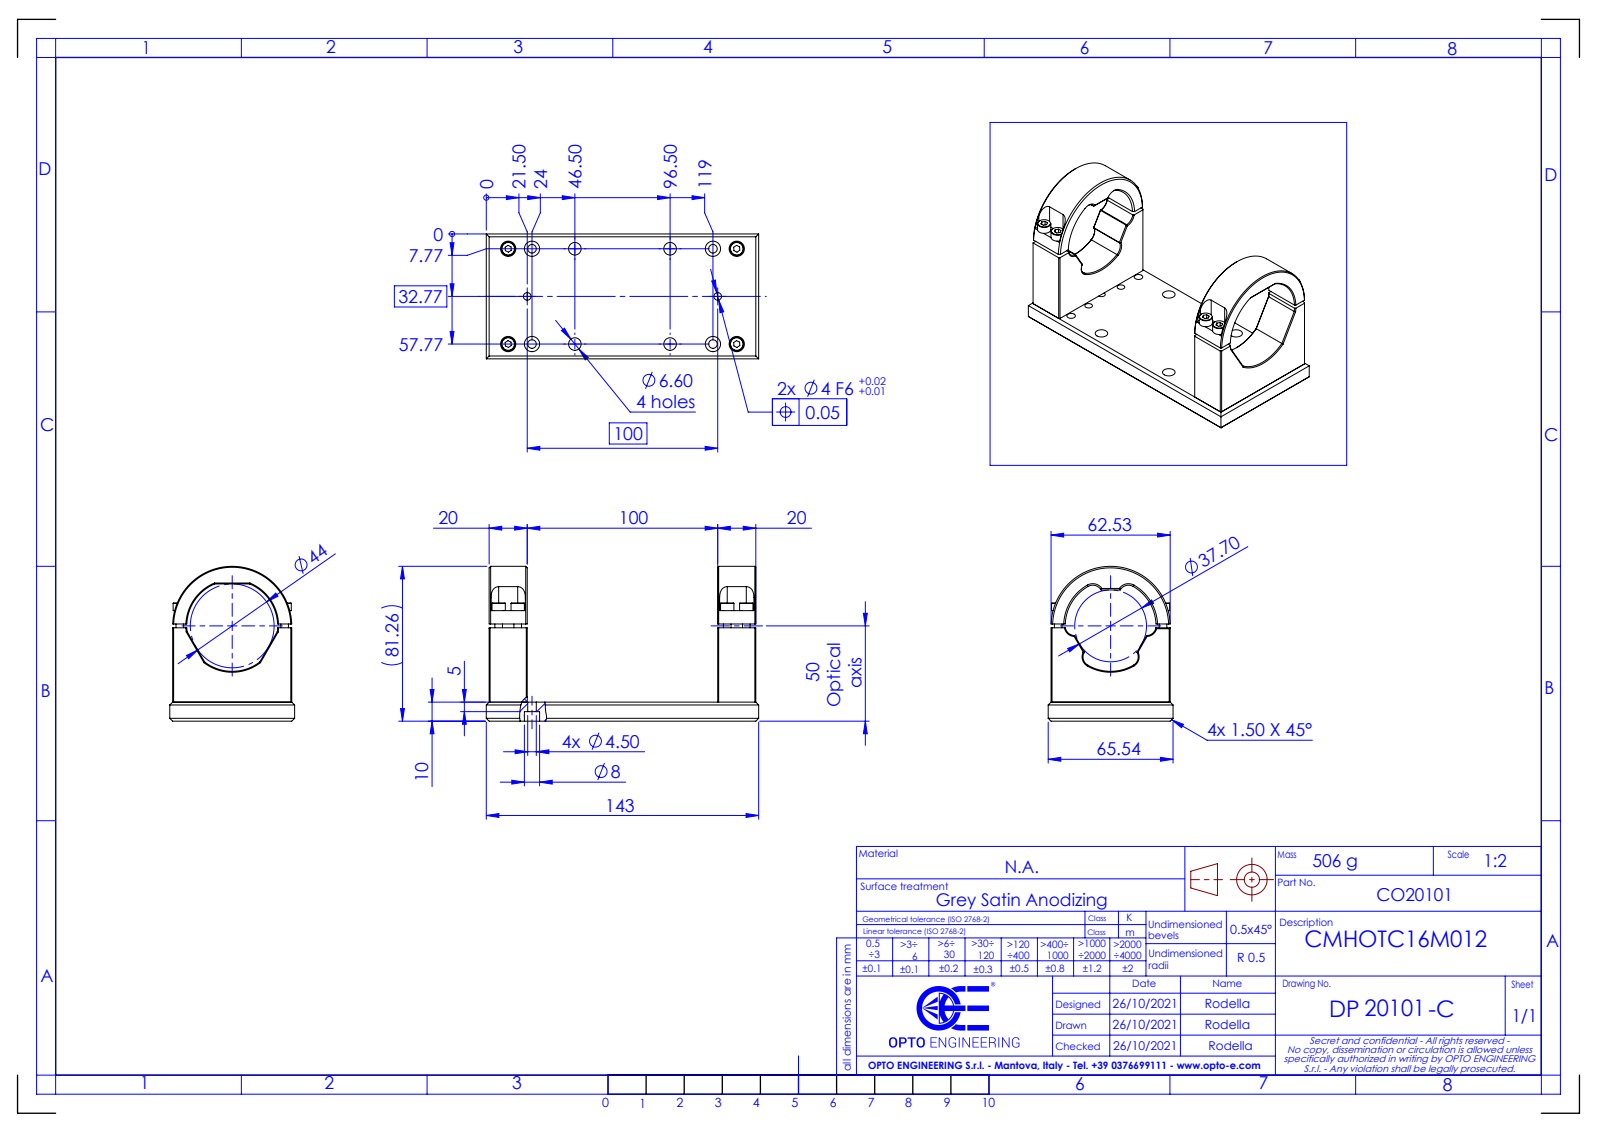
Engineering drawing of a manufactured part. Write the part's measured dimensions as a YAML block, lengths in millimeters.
part_name: "DP20101-C_CMHOTC16M012"
step_written_by: "SolidWorks 2021 (CONFIG_CONTROL_DESIGN)"
units: millimeters
bodies: {solids: 0, faces: 356, planar: 181, cylindrical: 117, other: 58}
overall_size: [143, 81.26, 65.54]
round_holes:
  - {diameter: 4.5, count: 12}
  - {diameter: 8, count: 8}
  - {diameter: 4, count: 6}
  - {diameter: 6.6, count: 4}
round_bosses_or_shafts:
  - {diameter: 7, count: 8}
  - {diameter: 4, count: 8}
partial_cylinders:
  - {radius: 4, count: 8}
  - {radius: 5, count: 6}
  - {radius: 23.85, count: 1}
  - {radius: 31.26, count: 1}
face_to_face_distances: [10, 20, 120, 100, 140, 1.51, 64.03, 62.52, 65.54, 1.5]
hole_center_spacings: [5.59, 50, 52.75, 120, 7.91, 10, 12.26, 12.5]
